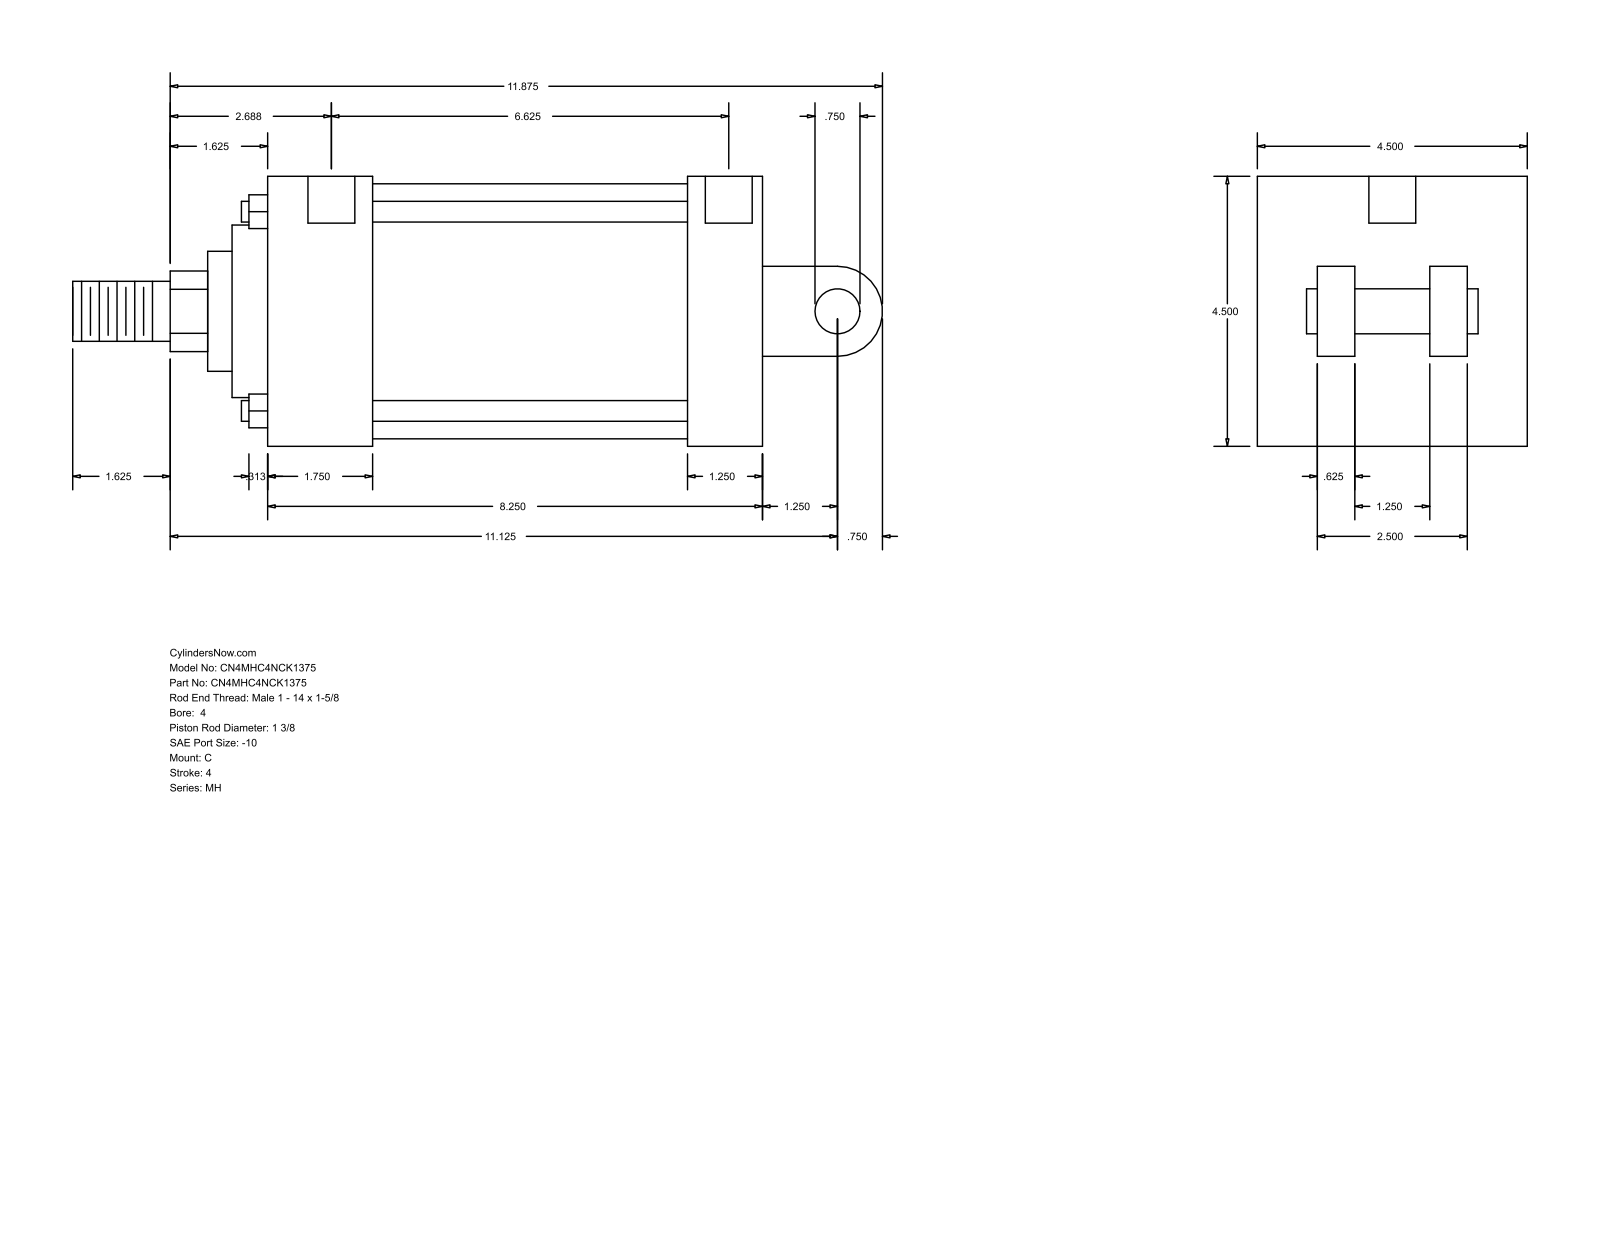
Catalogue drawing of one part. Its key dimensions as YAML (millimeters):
part_name: "MH_C__0400_1.375"
step_written_by: "GSSL Pune (CONFIG_CONTROL_DESIGN)"
units: millimeters
bodies: {solids: 0, faces: 101, planar: 71, cylindrical: 30, other: 0}
overall_size: [342.9, 114.3, 114.3]
round_holes:
  - {diameter: 8.73, count: 4}
  - {diameter: 19.84, count: 2}
round_bosses_or_shafts:
  - {diameter: 8.76, count: 4}
  - {diameter: 107.95, count: 1}
  - {diameter: 73.03, count: 1}
  - {diameter: 50.8, count: 1}
  - {diameter: 34.92, count: 1}
  - {diameter: 25.4, count: 1}
  - {diameter: 19.05, count: 1}
partial_cylinders:
  - {radius: 17.06, count: 1}
  - {radius: 19.05, count: 1}
face_to_face_distances: [114.3, 209.55, 44.45, 177.8, 133.35, 165.1, 31.75, 41.27, 73.03, 38.1]
hole_center_spacings: [171.45, 1.58, 1.59, 168.28, 169.86, 169.87]
